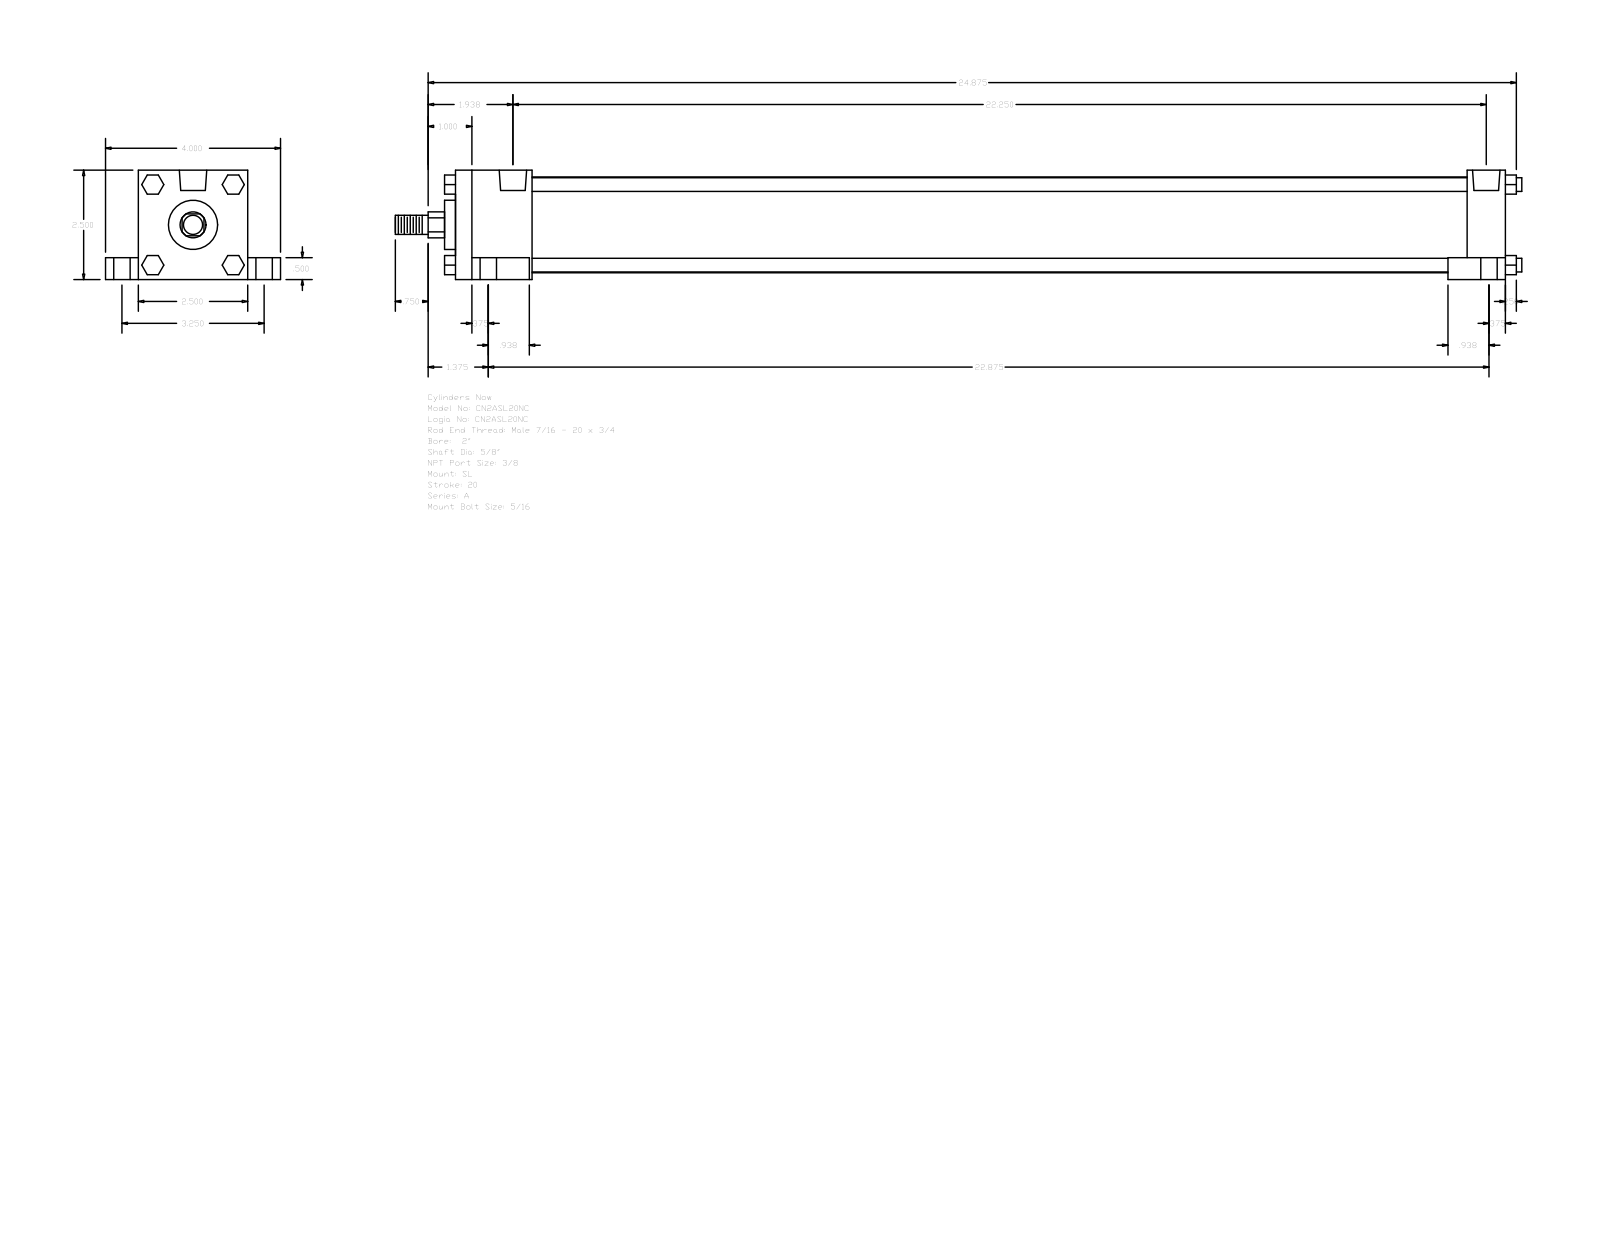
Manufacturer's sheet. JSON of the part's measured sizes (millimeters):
{"part_name": "A_SL__0200_0.625", "step_written_by": "GSSL Pune (CONFIG_CONTROL_DESIGN)", "units": "millimeters", "bodies": {"solids": 0, "faces": 148, "planar": 112, "cylindrical": 36, "other": 0}, "overall_size": [654.05, 101.6, 63.5], "round_holes": [[5.56, 4], [9.53, 4], [15.88, 4], [15.93, 2]], "round_bosses_or_shafts": [[7.94, 4], [55.63, 1], [28.57, 1], [15.88, 1], [11.11, 1]], "partial_cylinders_radius": [[7.54, 1]], "face_to_face_distances": [63.5, 609.6, 50.8, 12.7, 19.05, 82.55, 44.45, 565.15, 587.37, 542.92], "hole_center_spacings": [41.3, 41.64, 43.67, 45.13, 82.54, 557.2, 564.27, 568.24]}
